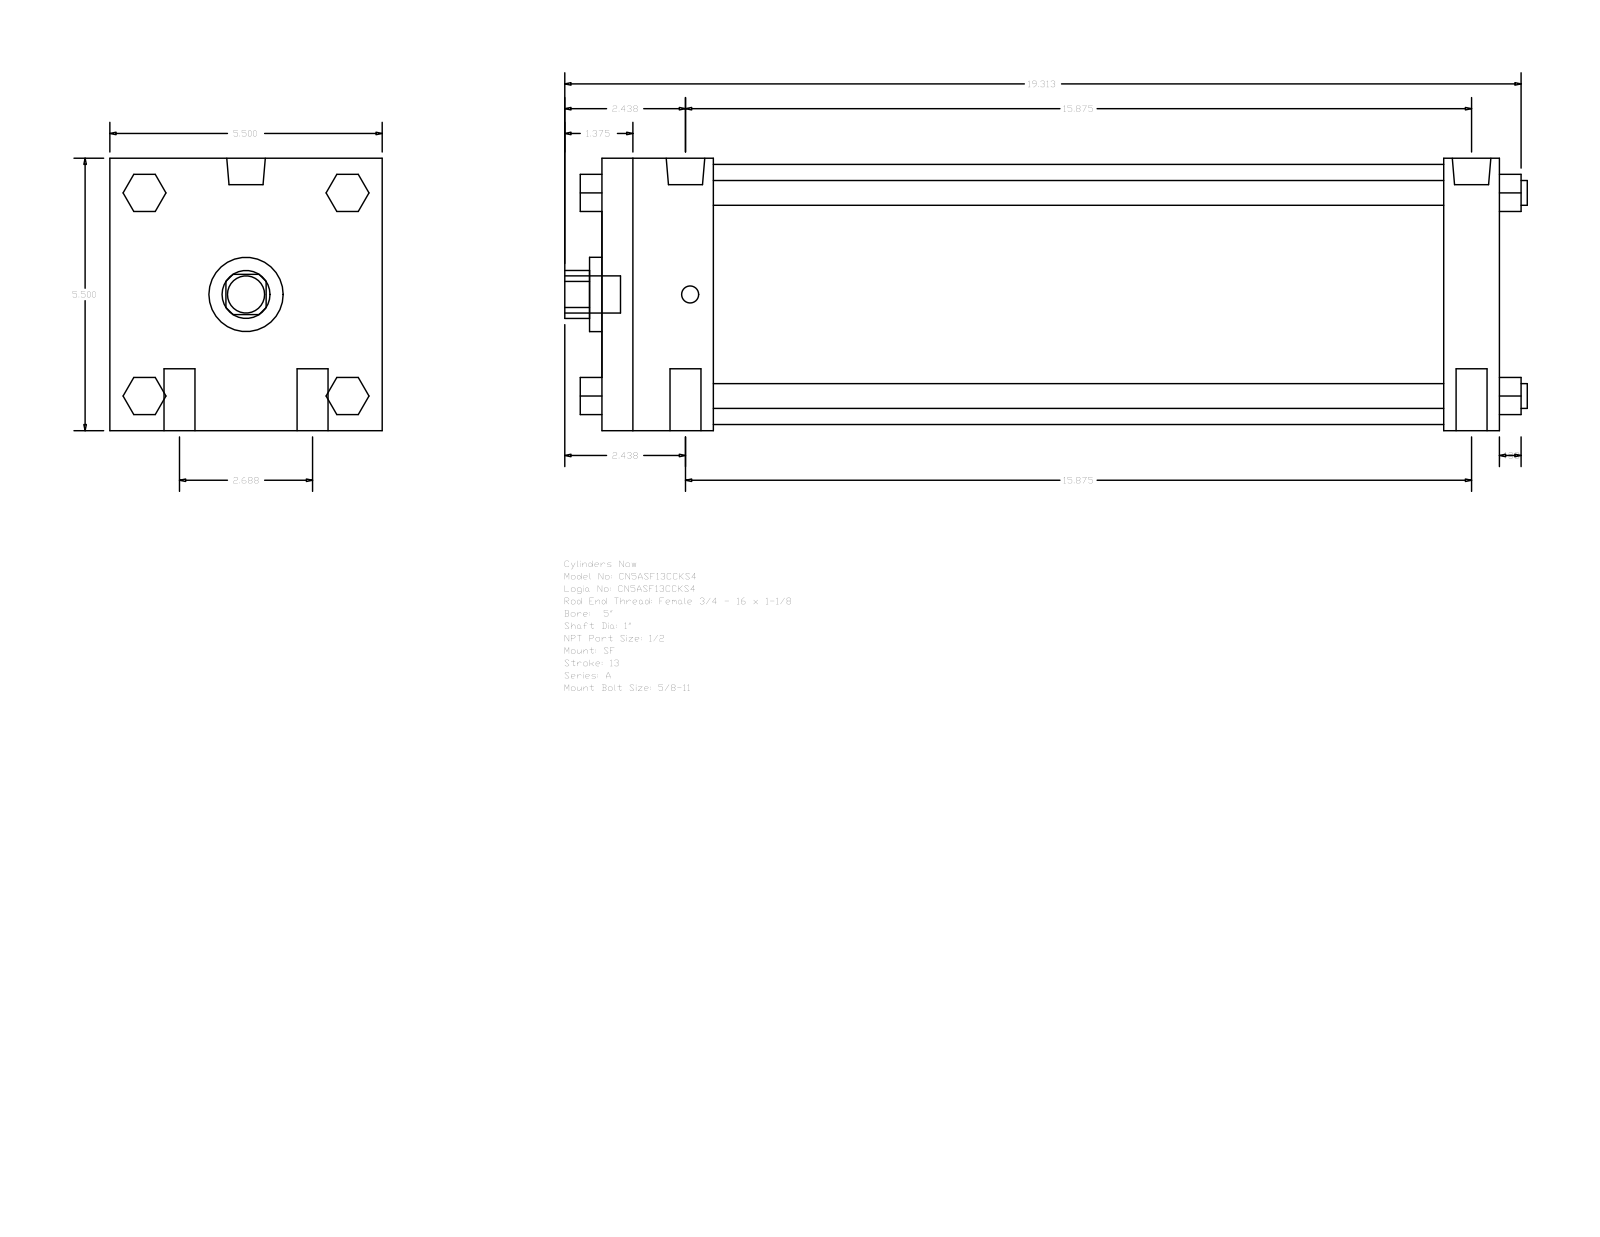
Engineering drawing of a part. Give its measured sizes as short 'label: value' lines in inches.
name: A_SF__0500_1
written by: GSSL Pune (CONFIG_CONTROL_DESIGN)
unit: in
bodies: 0 solids, 124 faces (94 planar, 30 cylindrical, 0 other)
size: 19.437 × 5.5 × 5.5
holes: 1× ⌀1, 1× ⌀1.5, 1× ⌀5.25
bosses: 4× ⌀0.625, 4× ⌀0.5, 2× ⌀0.778, 2× ⌀0.344, 1× ⌀0.75
rounds: 1× R0.484
face distances: 5.5, 18.125, 2.25, 17, 14.75, 15.875, 1.125, 0.75, 2.05, 3.55
